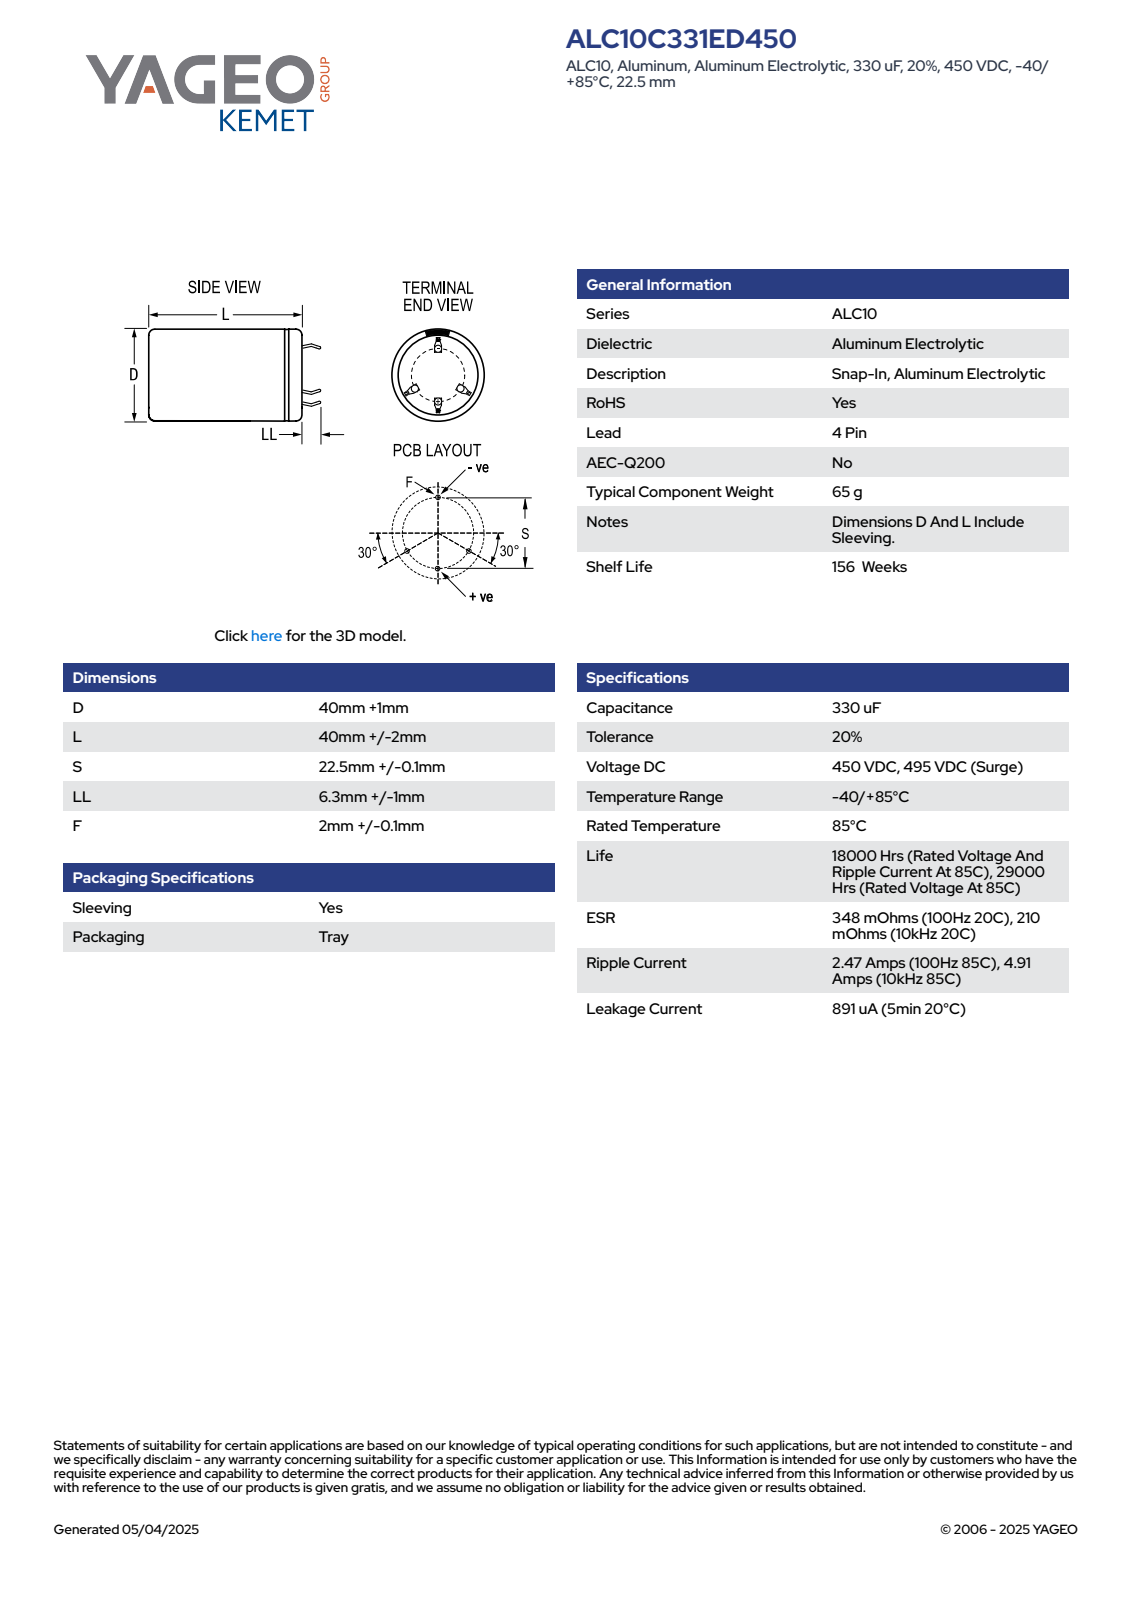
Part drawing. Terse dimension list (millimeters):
name: CARS_K4P_40X40_D41L42S22.5LL7.3F2.1
written by: SolidWorks 2014 (AUTOMOTIVE_DESIGN)
unit: mm
bodies: 1 solid, 134 faces (80 planar, 15 cylindrical, 39 other)
size: 49.29 × 41 × 41
volume: 54 679 mm³; area: 8 094 mm²
holes: 1× ⌀36.28
bosses: 1× ⌀41
rounds: 1× R20.49
face distances: 41.99, 42.49, 0.5, 0.4, 0.6, 20.19, 0.75, 1.35, 19.79, 20.59
